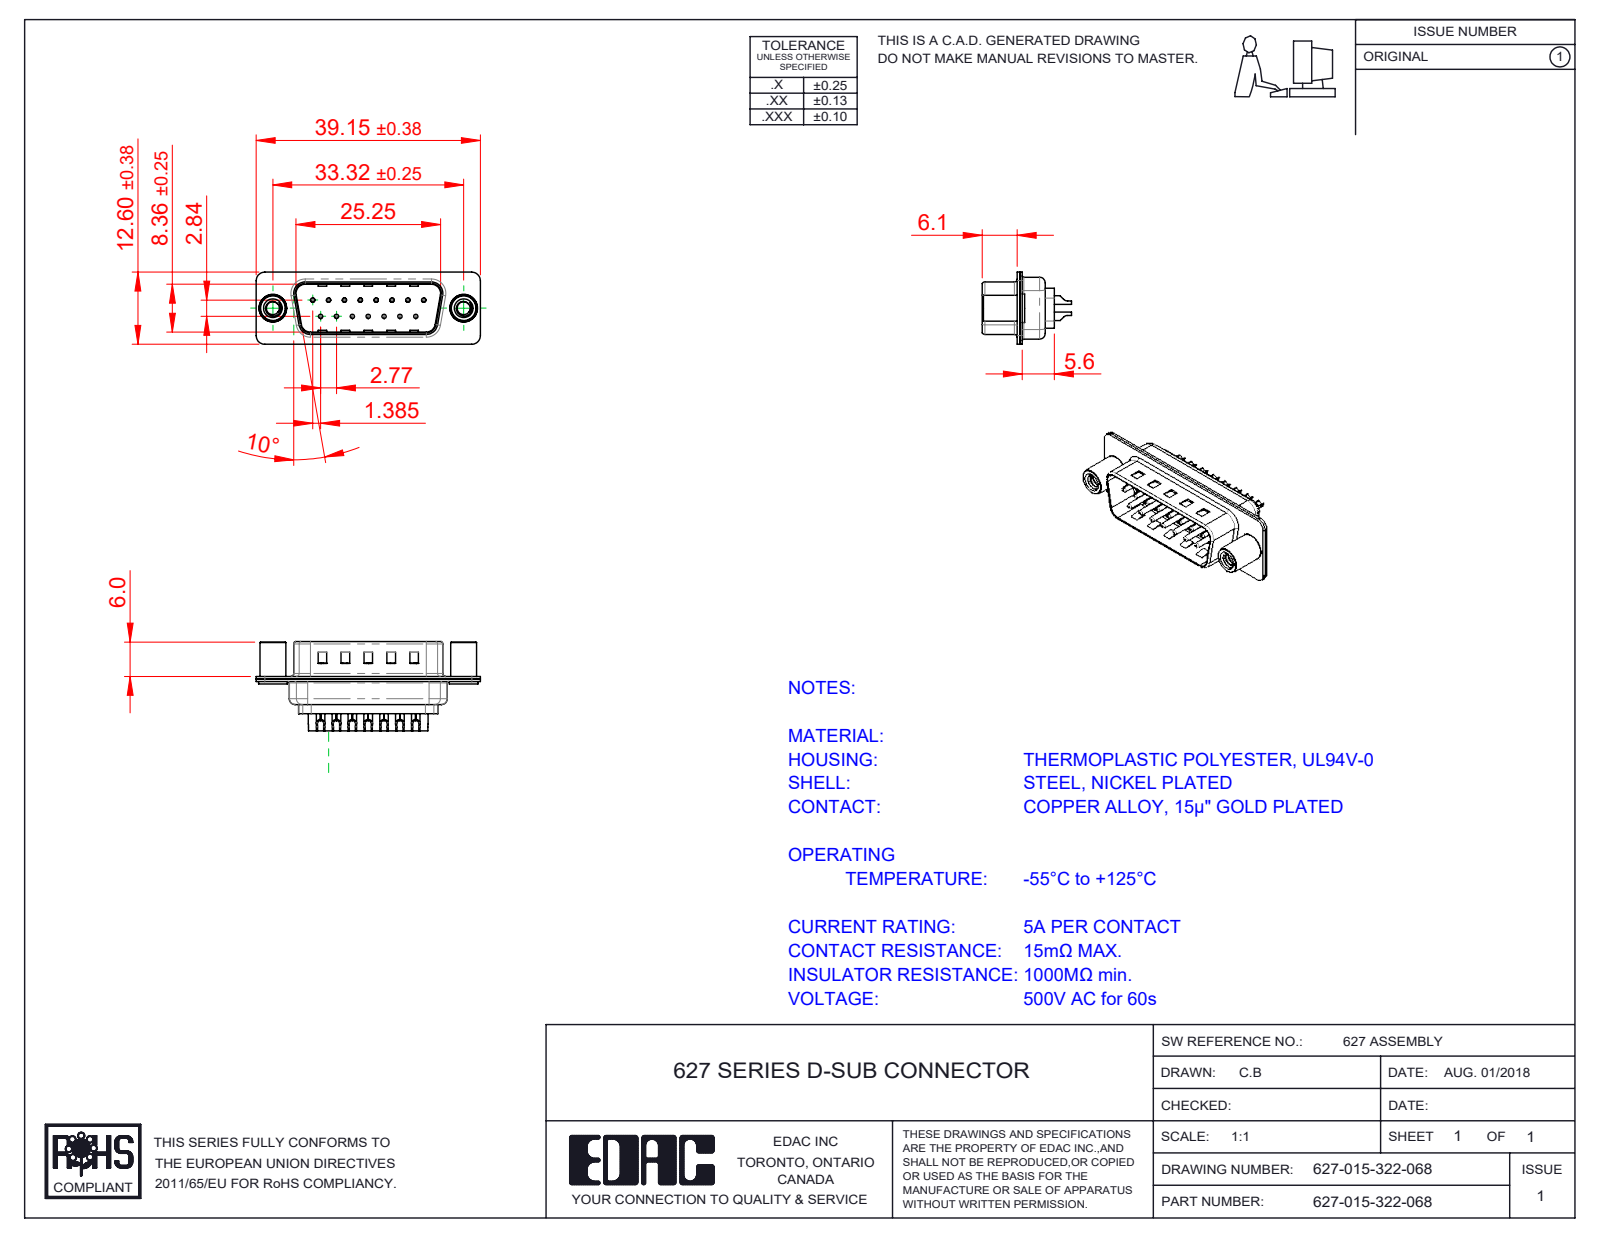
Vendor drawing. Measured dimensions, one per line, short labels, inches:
name: 627 4-40 Threaded Standoff; 627 Contact Row 1_22L; 627 Shell Front_15 Contacts; 627-015-322-068 (+3 more)
written by: SolidWorks 2020 (CONFIG_CONTROL_DESIGN)
unit: in
bodies: 20 solids, 1334 faces (351 planar, 596 cylindrical, 387 other)
size: 1.541 × 0.604 × 0.496
volume: 0.116 in³; area: 8.708 in²
holes: 15× ⌀0.014, 15× ⌀0.043, 15× ⌀0.063, 2× ⌀0.089, 2× ⌀0.157, 2× ⌀0.189
bosses: 15× ⌀0.079, 15× ⌀0.059, 15× ⌀0.03, 2× ⌀0.197, 2× ⌀0.193, 2× ⌀0.177
rounds: 16× R0.059, 12× R0.079, 8× R0.02, 8× R0.063, 6× R0.039, 4× R0.01, 4× R0.024, 4× R0.026
face distances: 0.016, 0.018, 0.035, 0.032, 0.377, 0.345, 0.059, 0.055, 0.256, 0.22
hole spacings: 0.124, 0.109, 0.218, 0.327, 0.436, 0.198, 0.198, 0.294
